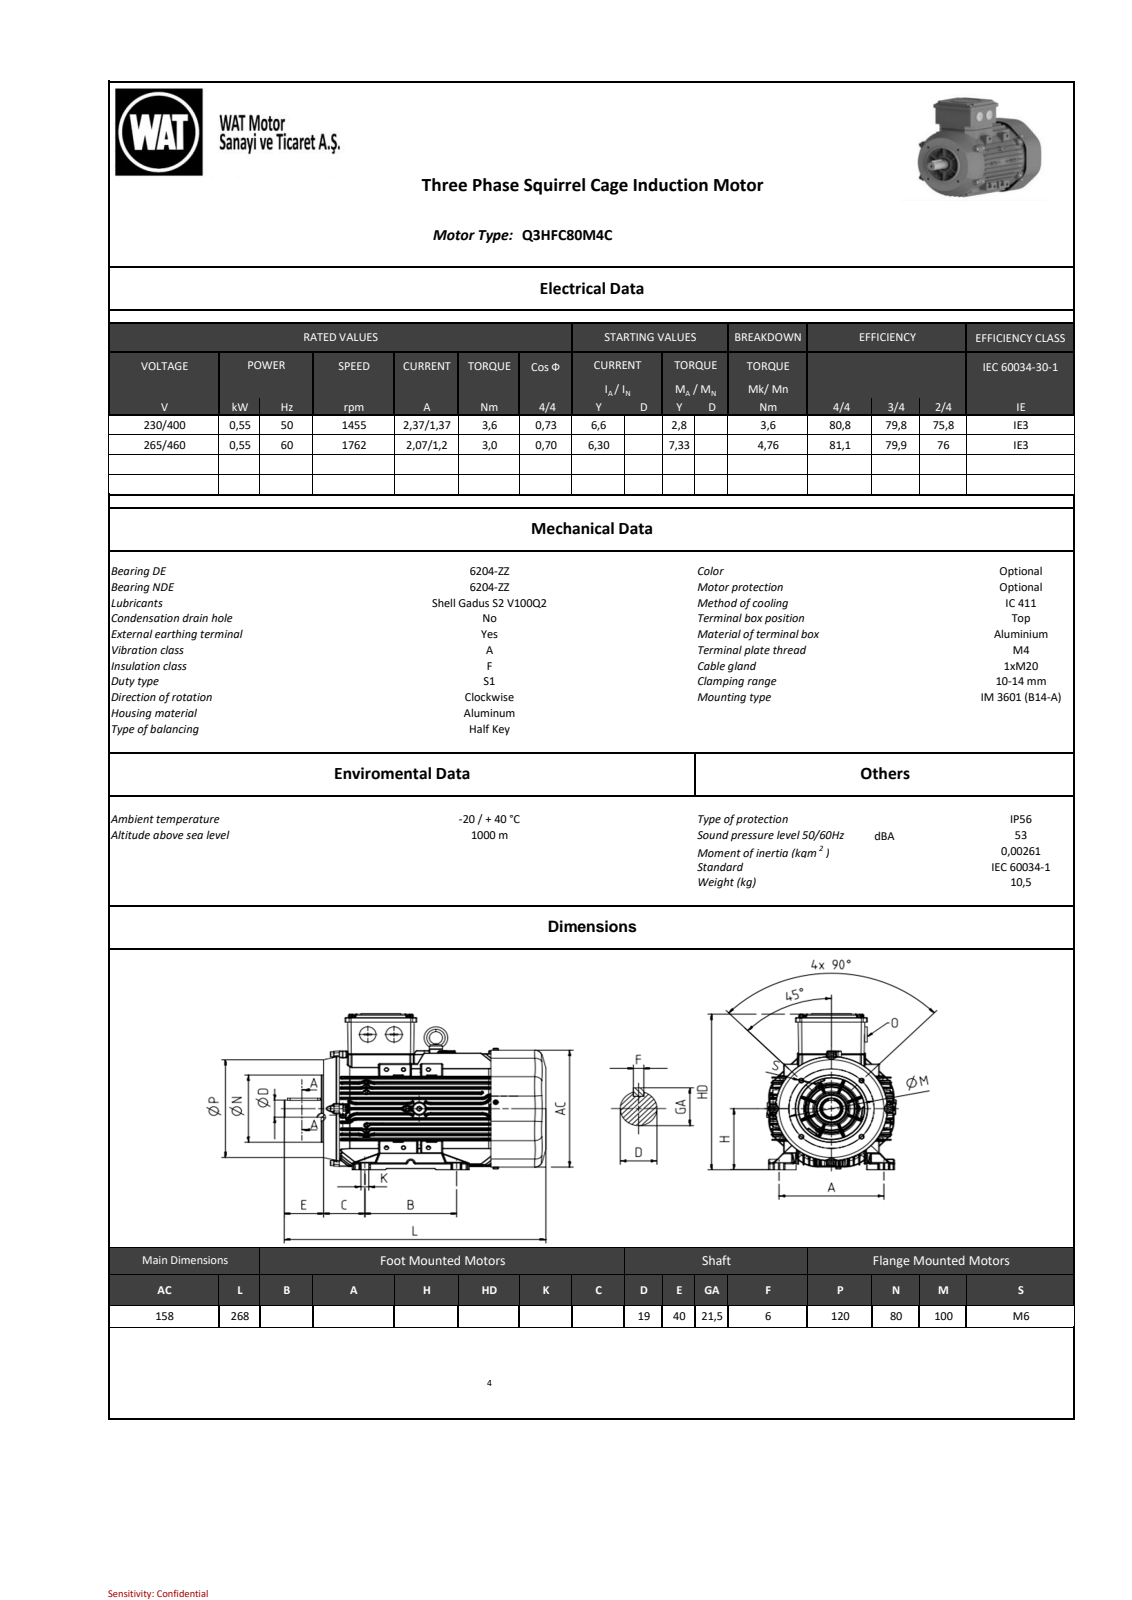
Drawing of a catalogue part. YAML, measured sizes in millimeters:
part_name: "model1_objects"
step_written_by: "SIEMENS PLM Software NX2206.8101 (AUTOMOTIVE_DESIGN)"
units: millimeters
bodies: {solids: 0, faces: 5032, planar: 1087, cylindrical: 2043, other: 1902}
overall_size: [268, 214.5, 158]
round_holes:
  - {diameter: 4.6, count: 2}
  - {diameter: 5, count: 1}
  - {diameter: 8, count: 1}
  - {diameter: 57, count: 1}
round_bosses_or_shafts:
  - {diameter: 6, count: 8}
  - {diameter: 8.33, count: 4}
  - {diameter: 21.38, count: 2}
  - {diameter: 146.5, count: 1}
  - {diameter: 80, count: 1}
  - {diameter: 61, count: 1}
  - {diameter: 24.07, count: 1}
  - {diameter: 20.2, count: 1}
partial_cylinders:
  - {radius: 0.5, count: 637}
  - {radius: 1, count: 440}
  - {radius: 0.8, count: 344}
  - {radius: 2, count: 55}
  - {radius: 0.5, count: 20}
  - {radius: 5, count: 12}
  - {radius: 75.75, count: 6}
  - {radius: 2, count: 4}
face_to_face_distances: [1, 157, 41.96, 156.98, 10.36, 86, 18, 10.49, 52.32, 20.84]
hole_center_spacings: [70.94]
